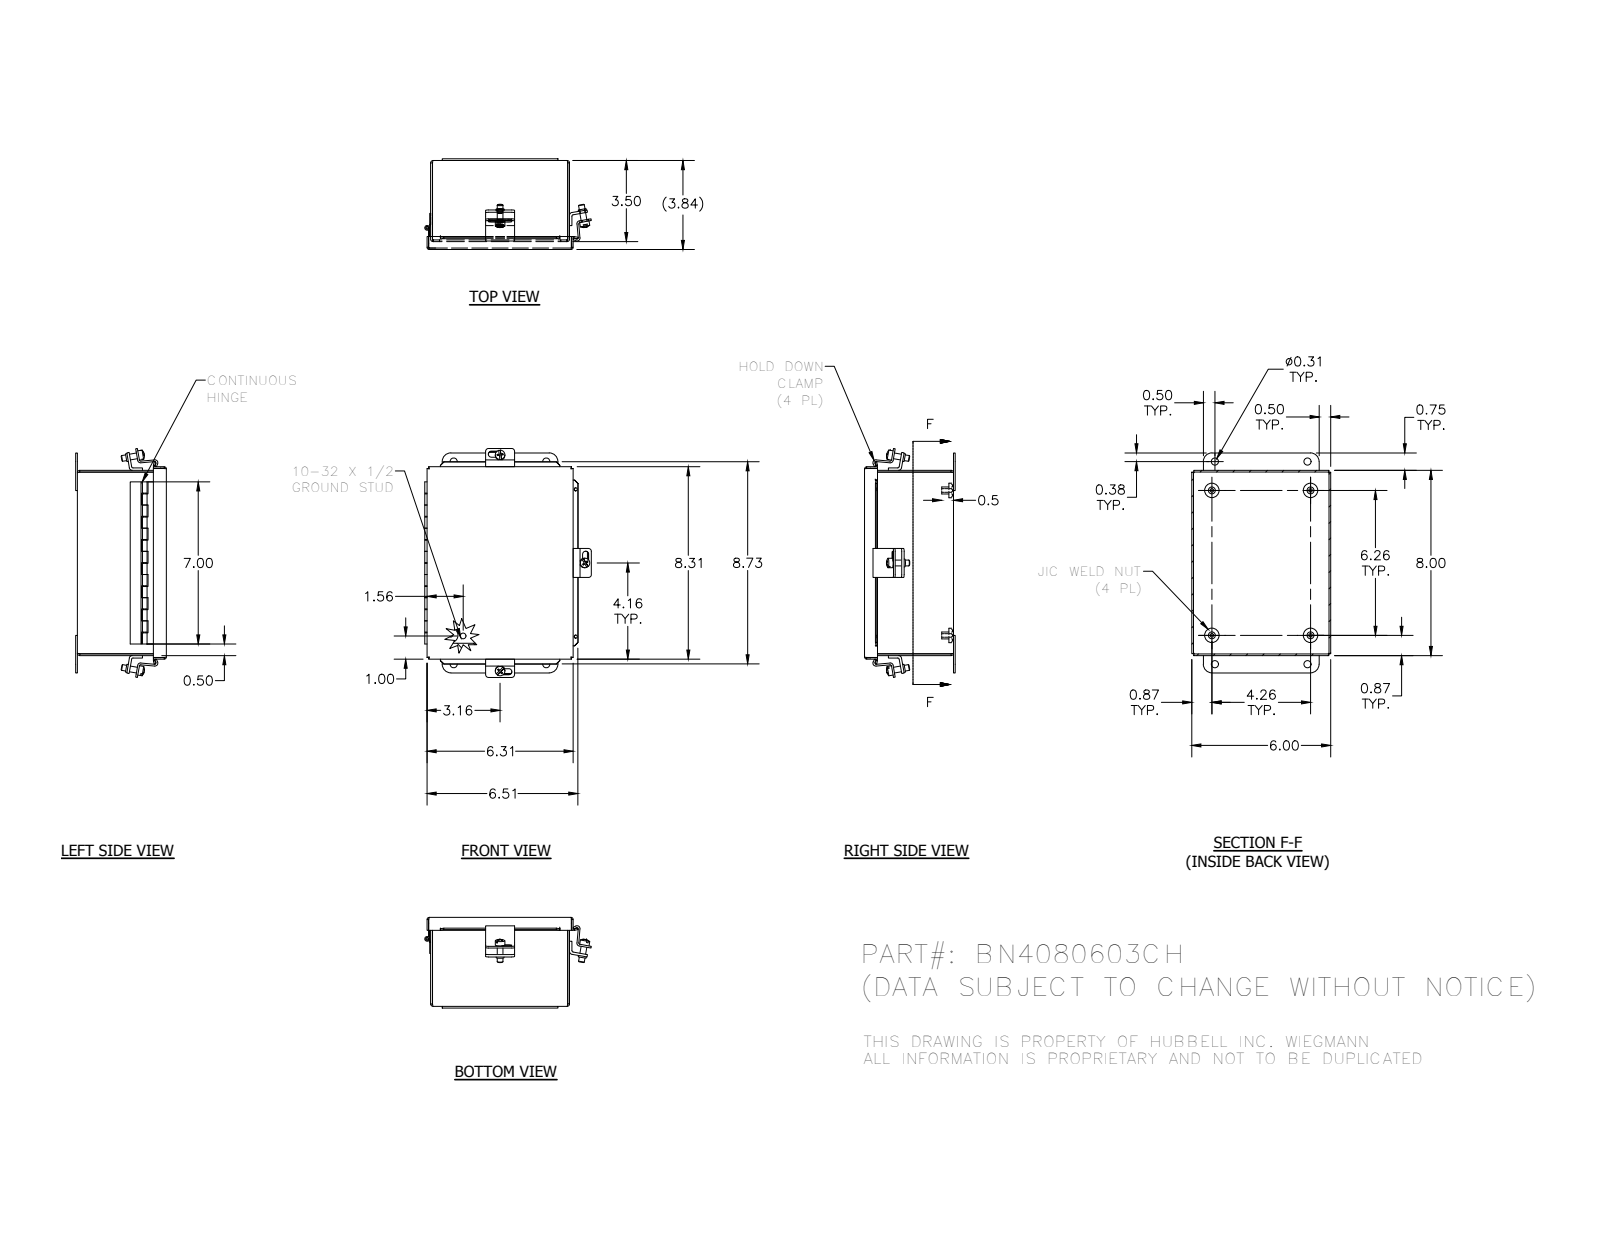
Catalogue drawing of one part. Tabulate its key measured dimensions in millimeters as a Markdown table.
| quantity | value |
| --- | --- |
| part name | B_0806CH_LID; 316162; 38811; 3499 (+8 more) |
| STEP written by | Autodesk Inventor 2016 (AUTOMOTIVE_DESIGN) |
| units | millimeters |
| bodies | 20 solids, 467 faces (301 planar, 115 cylindrical, 51 other) |
| overall size | 241.3 × 179.98 × 95.48 |
| volume | 341 489 mm³ |
| surface area | 368 404 mm² |
| round holes (diameter × count) | 3.96 × 4, 7.87 × 4, 3.56 × 2, 4.98 × 2, 2.96 × 1 |
| round bosses / shafts (diameter × count) | 15.88 × 4, 7.62 × 4, 6.35 × 3, 10.4 × 2, 8.74 × 2, 5.08 × 1, 4.83 × 1, 2.54 × 1 |
| partial cylindrical surfaces (radius × count) | 1.19 × 8, 3.07 × 8, 3.17 × 8, 1.98 × 4, 3.38 × 4, 3.48 × 4, 9.53 × 4, 0.79 × 3 |
| main face-to-face distances | 1.88, 92.08, 1.5, 150.52, 93.58, 90.2, 91.7, 201.32, 152.4, 148.64 |
| hole center spacings | 31.91, 109.48, 190.53, 217.41, 101.6, 107.95, 158.75, 191.98 |
